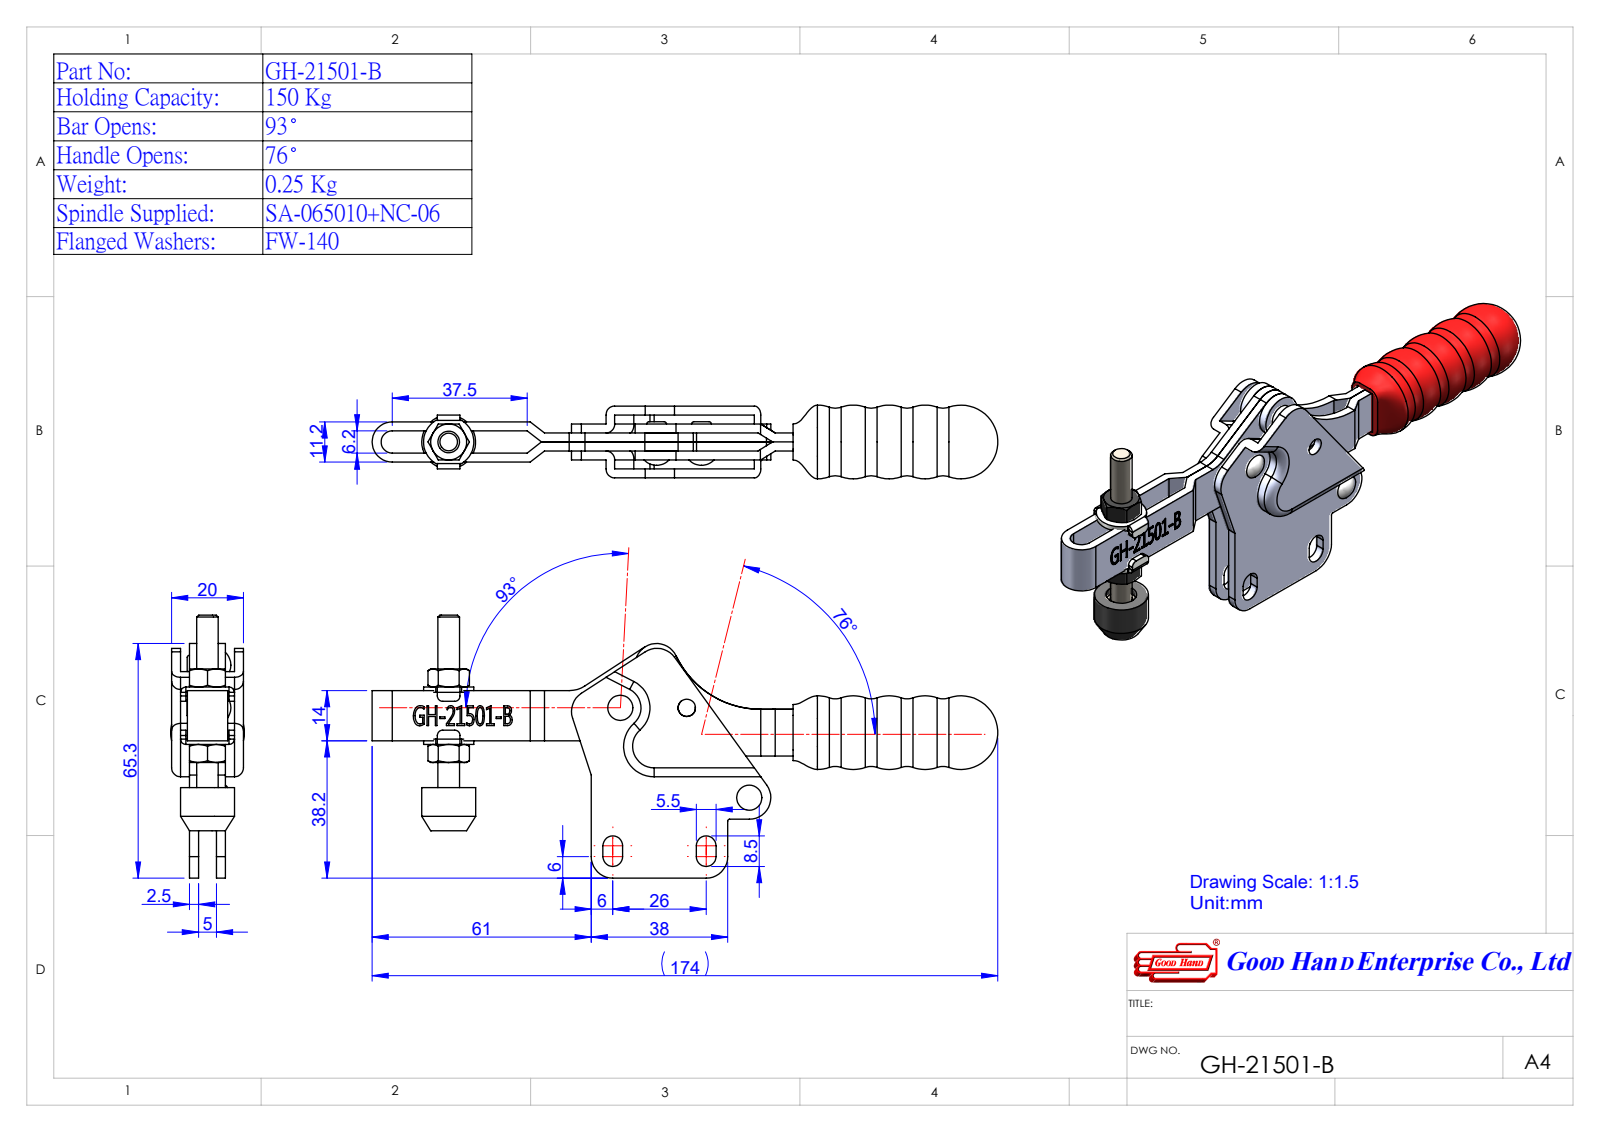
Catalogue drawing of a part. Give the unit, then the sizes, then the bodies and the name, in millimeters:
Units: millimetres
Overall size (bounding box): 173 × 73.2 × 20.5
Round holes (diameter × count): ⌀3 ×4, ⌀4.8 ×1
Round bosses / shafts (diameter × count): ⌀15 ×1, ⌀6 ×1
Partial cylindrical surfaces — rounded edges, fillets, slot ends (radius × count): R6 ×8, R1.5 ×4, R1.51 ×4, R2.75 ×4, R1 ×3, R8 ×2, R0.54 ×1, R3.1 ×1
Main face-to-face distances: 2.5, 5, 7.5, 10, 12.5, 15, 4.4, 13.1, 1.9, 10.6
Hole centre spacings: 8.46, 14.57, 15.61, 18.5, 22.06, 22.99, 23.78, 30.46
Volume: 46 056 mm³ · Surface area: 29 506 mm²
Bodies: 5 solids, 340 faces (142 planar, 124 cylindrical, 74 other)
Part name (STEP PRODUCT): GH-21501-B(簡化); 121502B08-1^GH-21501-B(簡化); Group2^GH-21501-B(簡化); Group4^GH-21501-B(簡化) (+2 more)
STEP written by: SolidWorks 2016 (AUTOMOTIVE_DESIGN)
